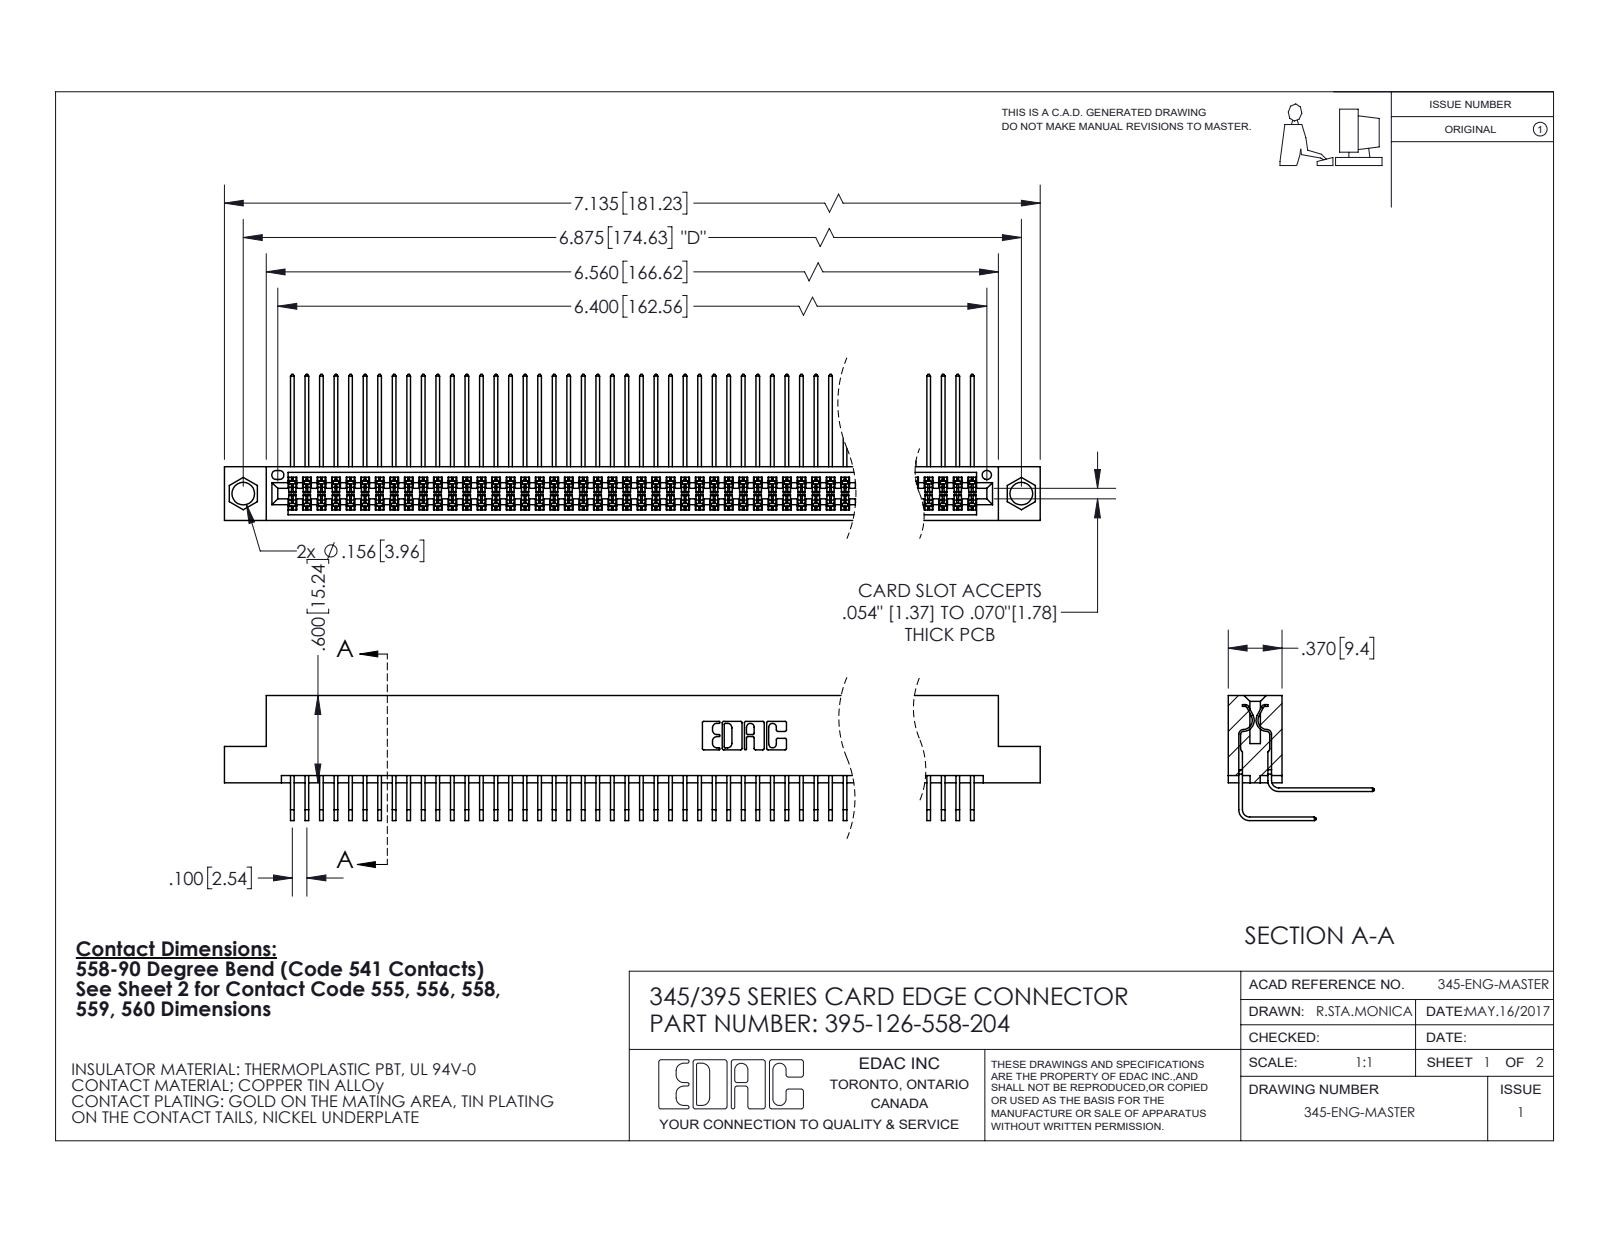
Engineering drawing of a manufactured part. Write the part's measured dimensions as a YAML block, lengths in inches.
part_name: "345-292-001_558 Tail - 2; 345 Part_Flush Mounting Lugs - 0.156 Dia-TI; 395-126-558-204; 345-292-001_558 559 Tail - 1"
step_written_by: "SolidWorks 2020 (CONFIG_CONTROL_DESIGN)"
units: inches
bodies: {solids: 127, faces: 6692, planar: 4504, cylindrical: 2188, other: 0}
overall_size: [7.135, 1.005, 0.859]
volume: 1.124
surface_area: 47.9
round_holes:
  - {diameter: 0.156, count: 2}
  - {diameter: 0.064, count: 1}
partial_cylinders:
  - {radius: 0.006, count: 252}
  - {radius: 0.01, count: 22}
  - {radius: 0.007, count: 6}
  - {radius: 0.031, count: 6}
  - {radius: 0.026, count: 3}
  - {radius: 0.014, count: 2}
  - {radius: 0.019, count: 2}
  - {radius: 0.022, count: 2}
face_to_face_distances: [0.072, 0.298, 0.2, 0.37, 0.098, 0.272, 0.025, 0.225, 0.025, 0.175]
hole_center_spacings: [0.27, 6.639, 6.875]
